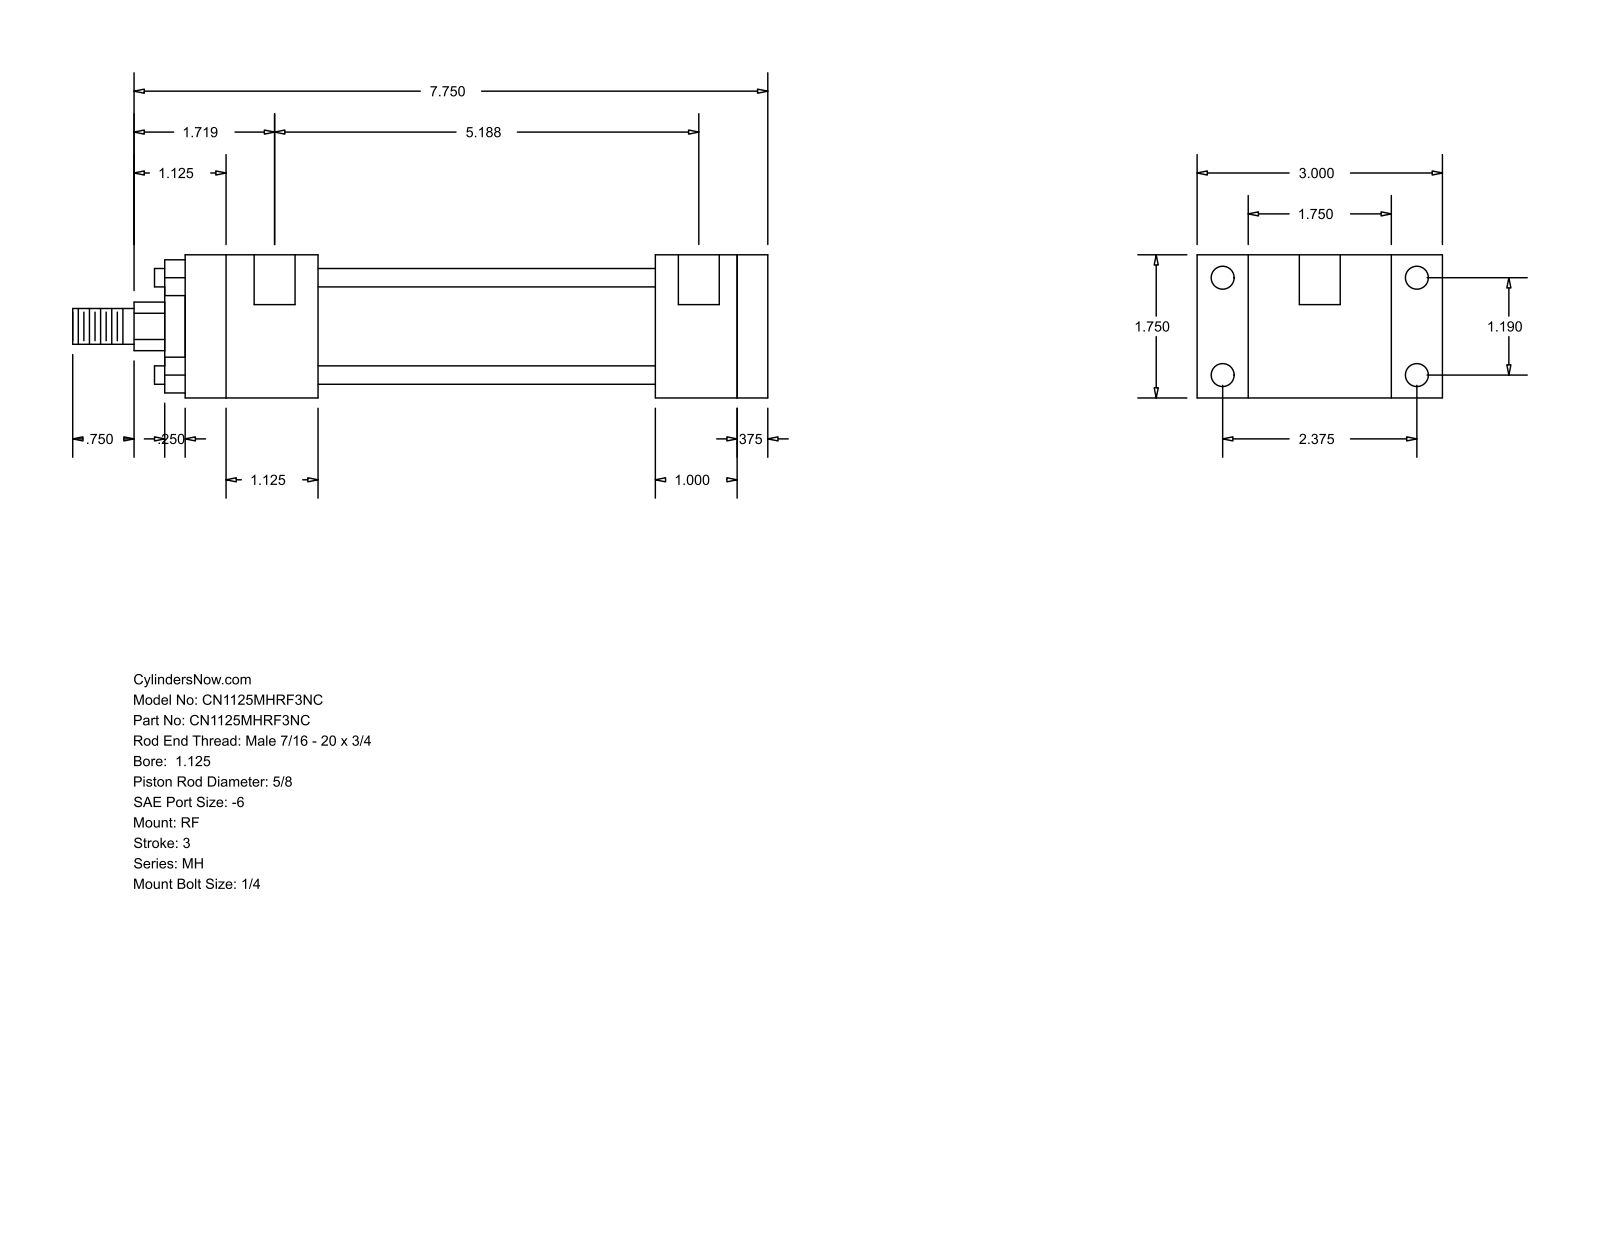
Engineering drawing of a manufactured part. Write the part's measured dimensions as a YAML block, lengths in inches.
part_name: "MH_RF__0112_0.625"
step_written_by: "GSSL Pune (CONFIG_CONTROL_DESIGN)"
units: inches
bodies: {solids: 0, faces: 92, planar: 64, cylindrical: 28, other: 0}
overall_size: [8.5, 3, 1.75]
round_holes:
  - {diameter: 0.219, count: 4}
  - {diameter: 0.281, count: 4}
  - {diameter: 0.5, count: 2}
round_bosses_or_shafts:
  - {diameter: 0.225, count: 4}
  - {diameter: 1.375, count: 1}
  - {diameter: 1.125, count: 1}
  - {diameter: 0.625, count: 1}
  - {diameter: 0.437, count: 1}
partial_cylinders:
  - {radius: 0.297, count: 1}
face_to_face_distances: [1.75, 0.375, 7.125, 0.625, 5.125, 5.5, 4.125, 1, 1.375, 1.625]
hole_center_spacings: [1.19, 2.375, 2.656, 5.063, 0.125, 5.187]
